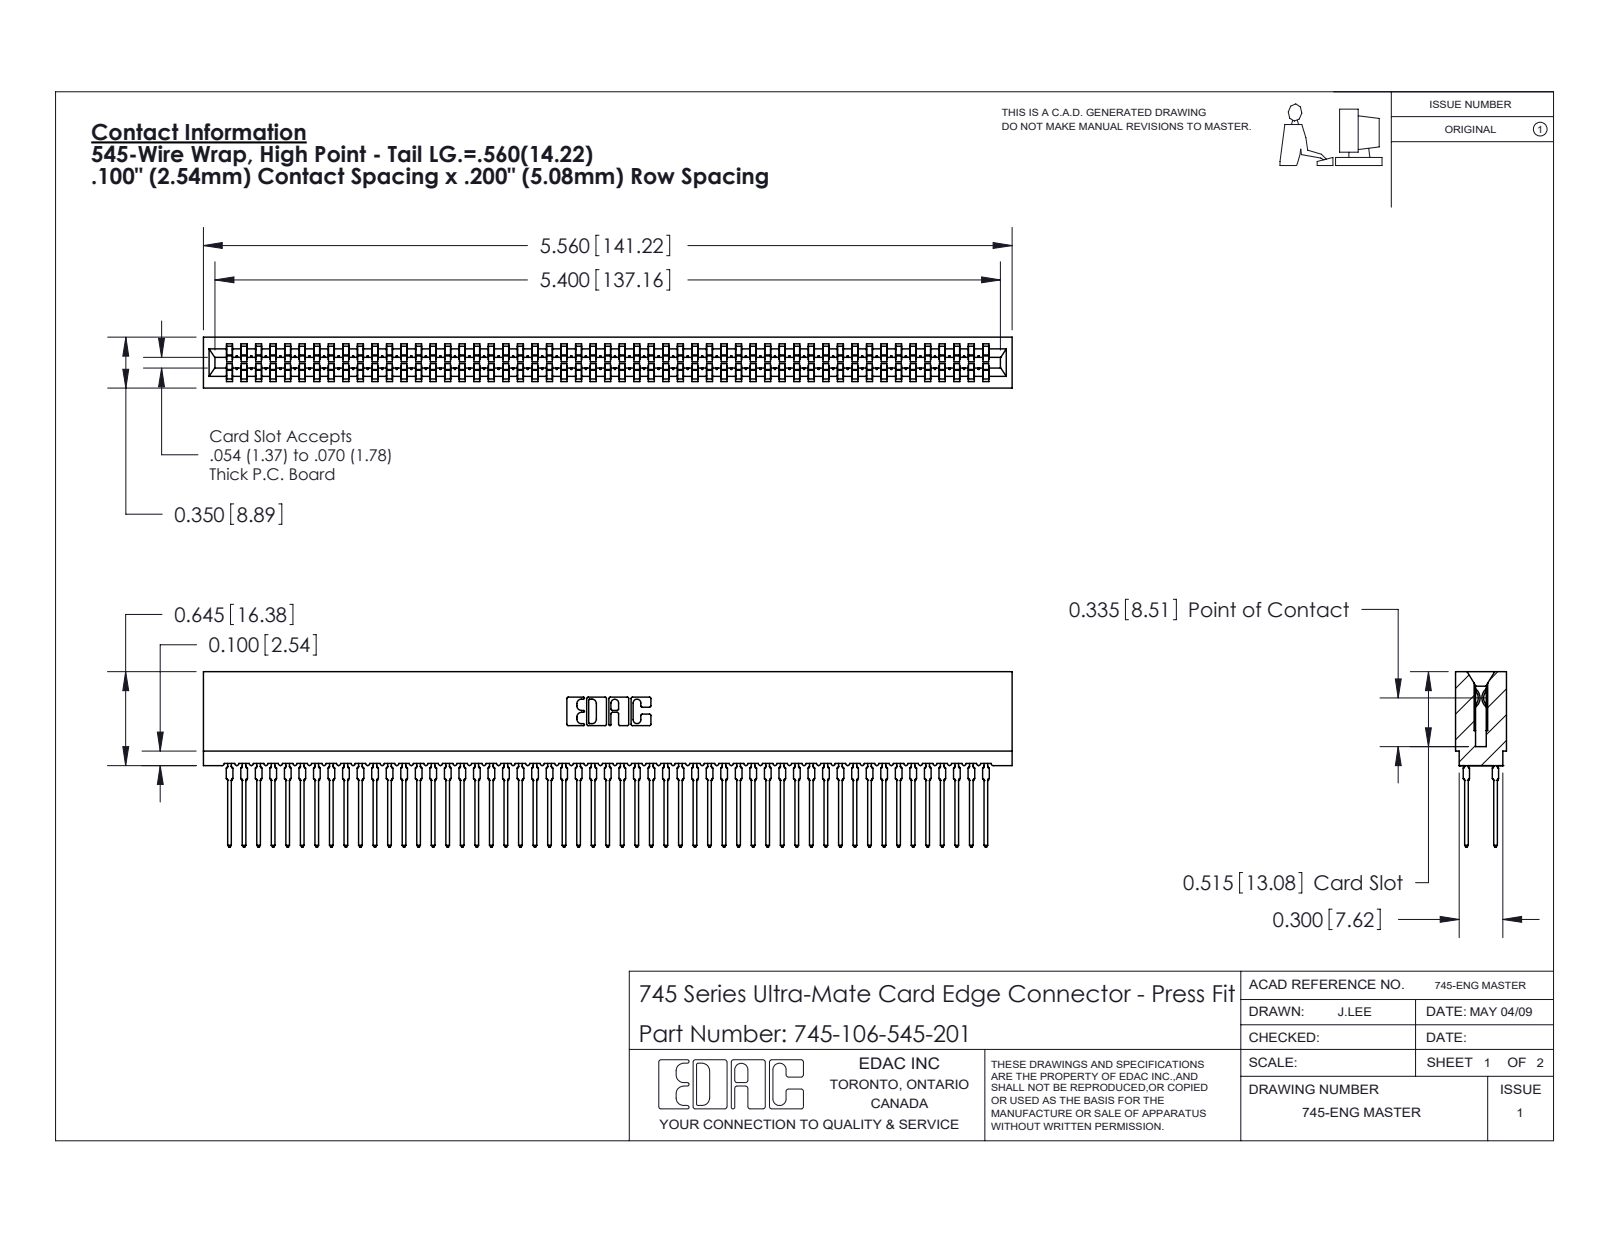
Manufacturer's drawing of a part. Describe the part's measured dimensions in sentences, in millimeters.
The part is named "745-106-545-201; 745-292-001_545; 745 Part_Insulator Option - 01". Its 3-D file was written by "SolidWorks 2020 (CONFIG_CONTROL_DESIGN)". It is 107 solids with 9582 faces: 4931 planar, 1895 cylindrical and 2756 other. Overall it measures 141.2 by 30.6 by 8.9 millimeters. Its volume is 13 000 cubic millimeters and its surface area 28 350 square millimeters. Partial cylindrical surfaces (rounded edges, fillets, slot ends): 212 of radius 0.5, 106 of radius 0.4, 22 of radius 0.3, 8 of radius 0.1, 8 of radius 0.3, 6 of radius 0.2, 6 of radius 0.8, 3 of radius 0.7. The main face-to-face distances are 1.6, 7.3, 8.9, 5.1, 1.1, 7.7, 0.5, 6.2, 3.5, 5.4.
